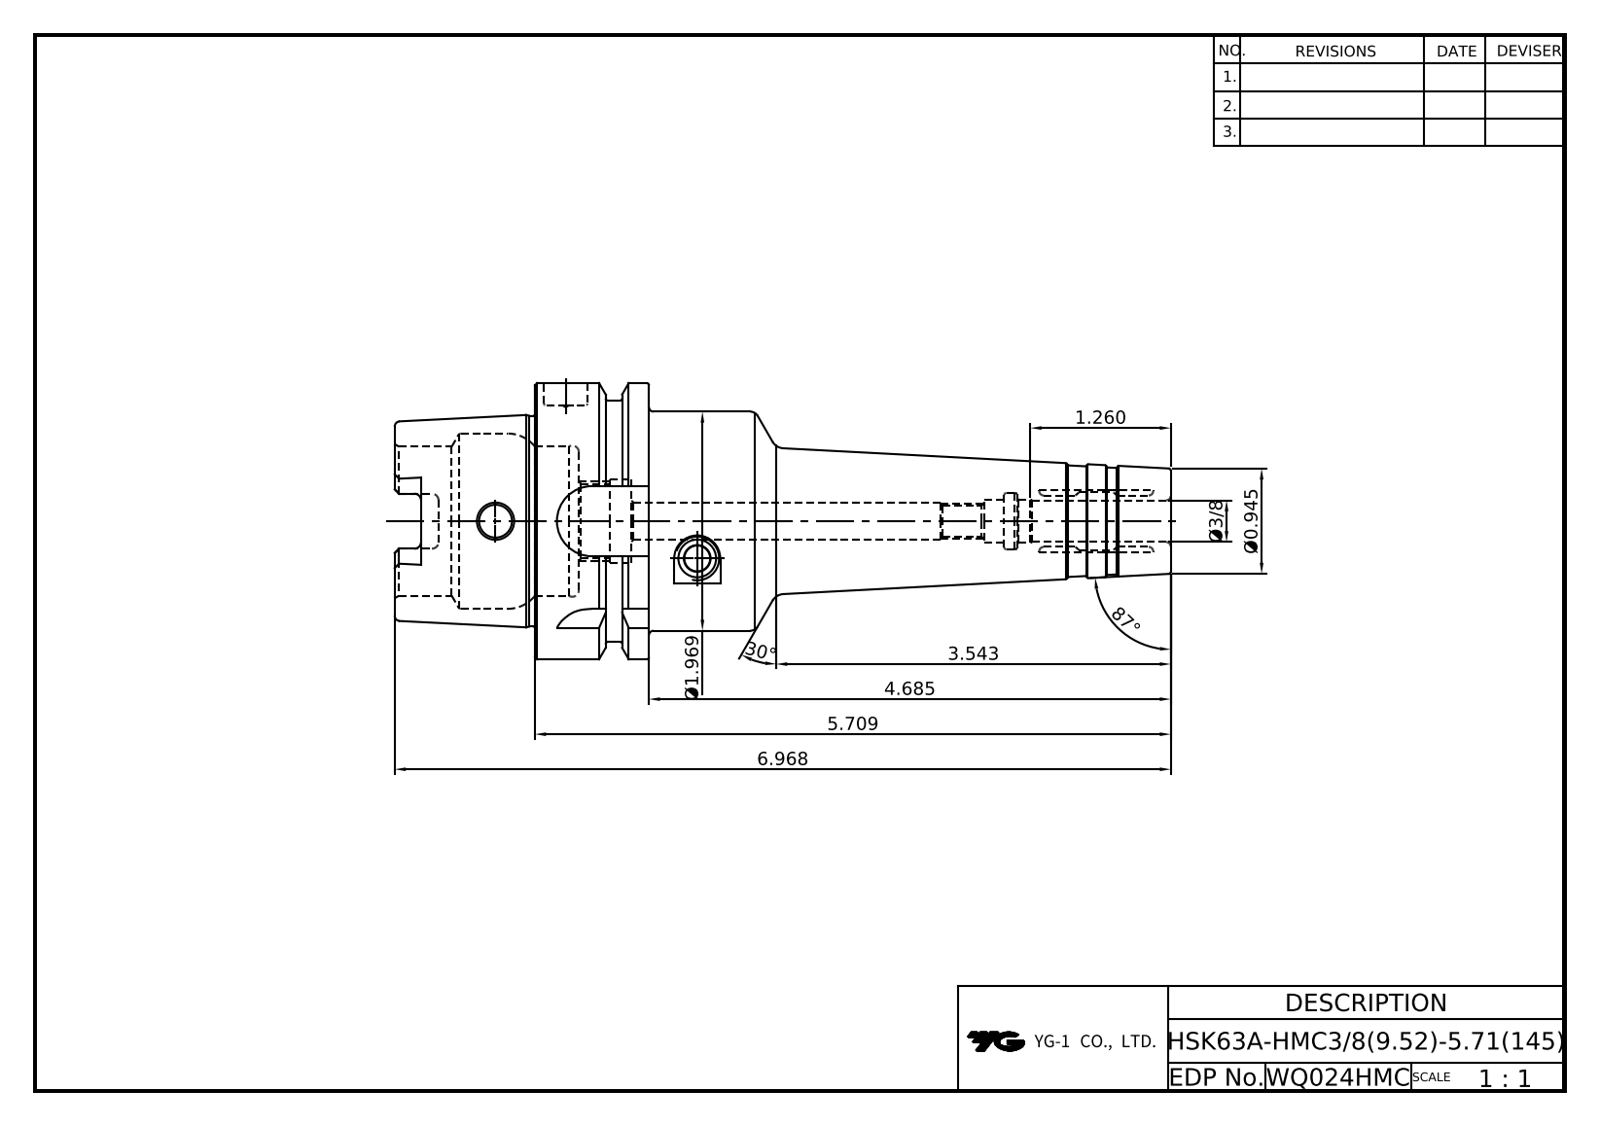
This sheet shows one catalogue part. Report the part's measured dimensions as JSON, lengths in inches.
{"part_name": "HSK63A-HMC3_8-5_71", "step_written_by": "CREO PARAMETRIC BY PTC INC, 2018100 (CONFIG_CONTROL_DESIGN)", "units": "inches", "bodies": {"solids": 1, "faces": 176, "planar": 55, "cylindrical": 51, "other": 70}, "overall_size": [6.969, 2.48, 2.48], "volume_in3": 11.49, "surface_area_in2": 58.01, "round_holes": [[0.394, 2], [0.272, 1], [0.295, 1], [0.315, 1], [0.375, 1], [0.669, 1], [0.709, 1], [0.748, 1], [1.339, 1], [1.575, 1]], "round_bosses_or_shafts": [[2.48, 1], [2.165, 1], [1.969, 1], [1.891, 1]], "partial_cylinders_radius": [[0.059, 6], [0.113, 4], [0.315, 4]], "face_to_face_distances": [1.024, 0.394, 0.63, 1.26, 0.241, 0.389, 1.654, 2.283, 0.157, 6.969]}
